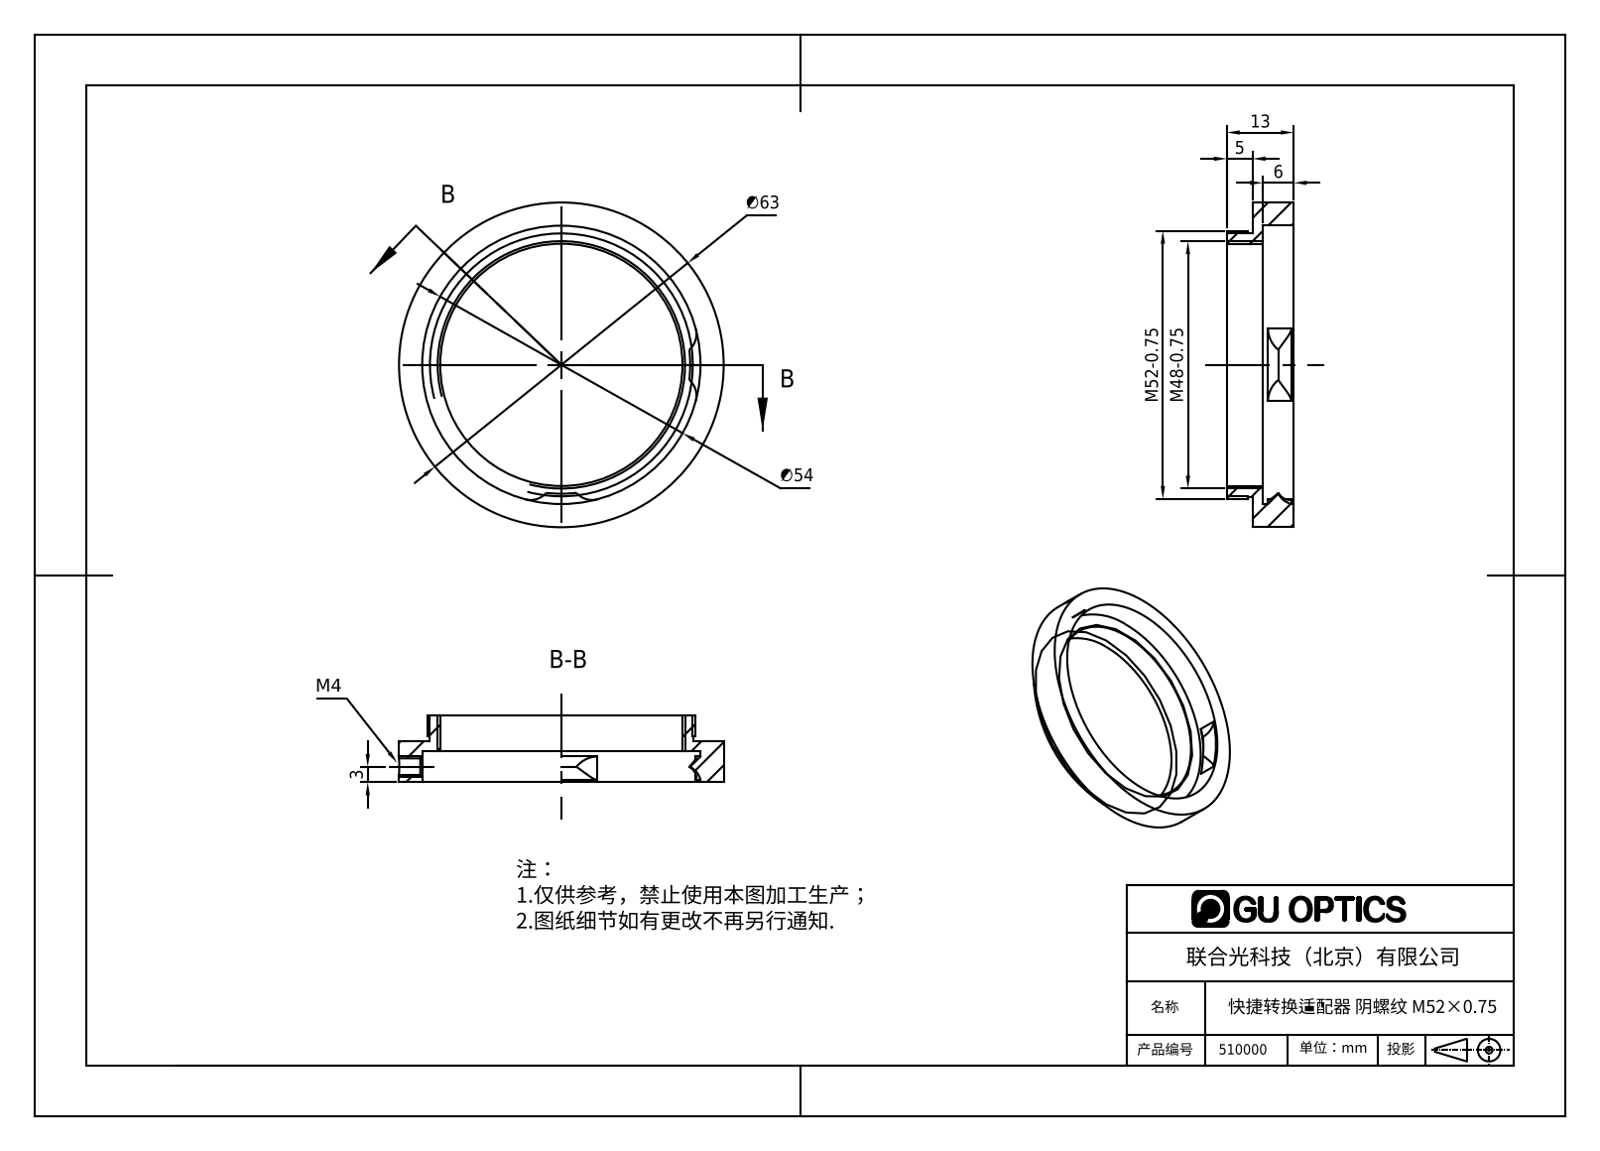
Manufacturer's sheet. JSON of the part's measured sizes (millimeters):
{"part_name": "510000", "step_written_by": "SolidWorks 2016 (CONFIG_CONTROL_DESIGN)", "units": "millimeters", "bodies": {"solids": 1, "faces": 30, "planar": 5, "cylindrical": 19, "other": 6}, "overall_size": [63, 63, 13], "volume_mm3": 9640, "surface_area_mm2": 7398, "round_holes": [[3.3, 1], [4.05, 1], [47, 1], [54, 1]], "round_bosses_or_shafts": [[63, 1], [52, 1], [51.2, 1]], "partial_cylinders_radius": [[4, 4]], "face_to_face_distances": [8, 2, 6, 5, 7, 13, 4, 1, 3, 9]}
